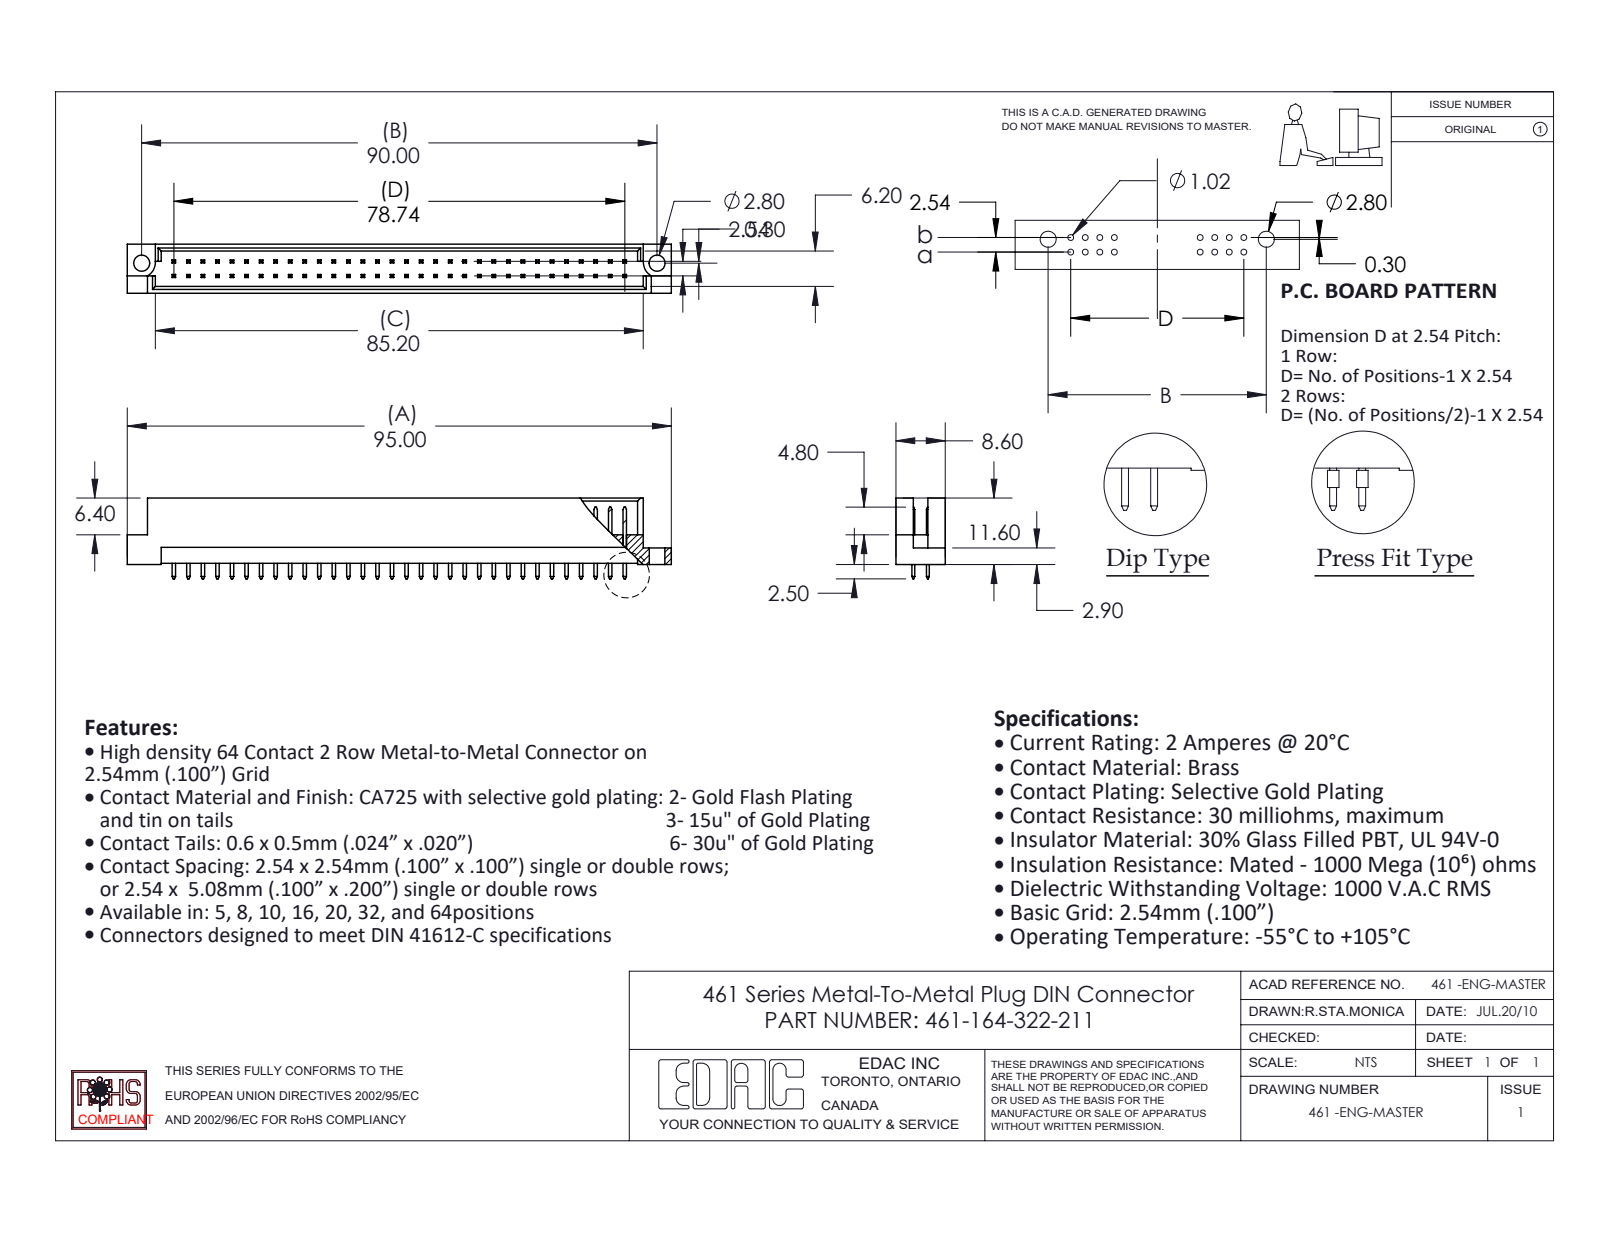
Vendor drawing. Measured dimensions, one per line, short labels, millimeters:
name: 461-164-322-211; 461 Part_64; 461-290_22
written by: SolidWorks 2020 (CONFIG_CONTROL_DESIGN)
unit: mm
bodies: 65 solids, 1201 faces (1194 planar, 7 cylindrical, 0 other)
size: 95 × 14.1 × 8.6
volume: 4 889 mm³; area: 7 407 mm²
holes: 2× ⌀2.8
rounds: 2× R2.8
face distances: 1.2, 7.4, 8.6, 2.54, 6.2, 3.28, 5.32, 2.08, 4.12, 2.78
hole spacings: 90
